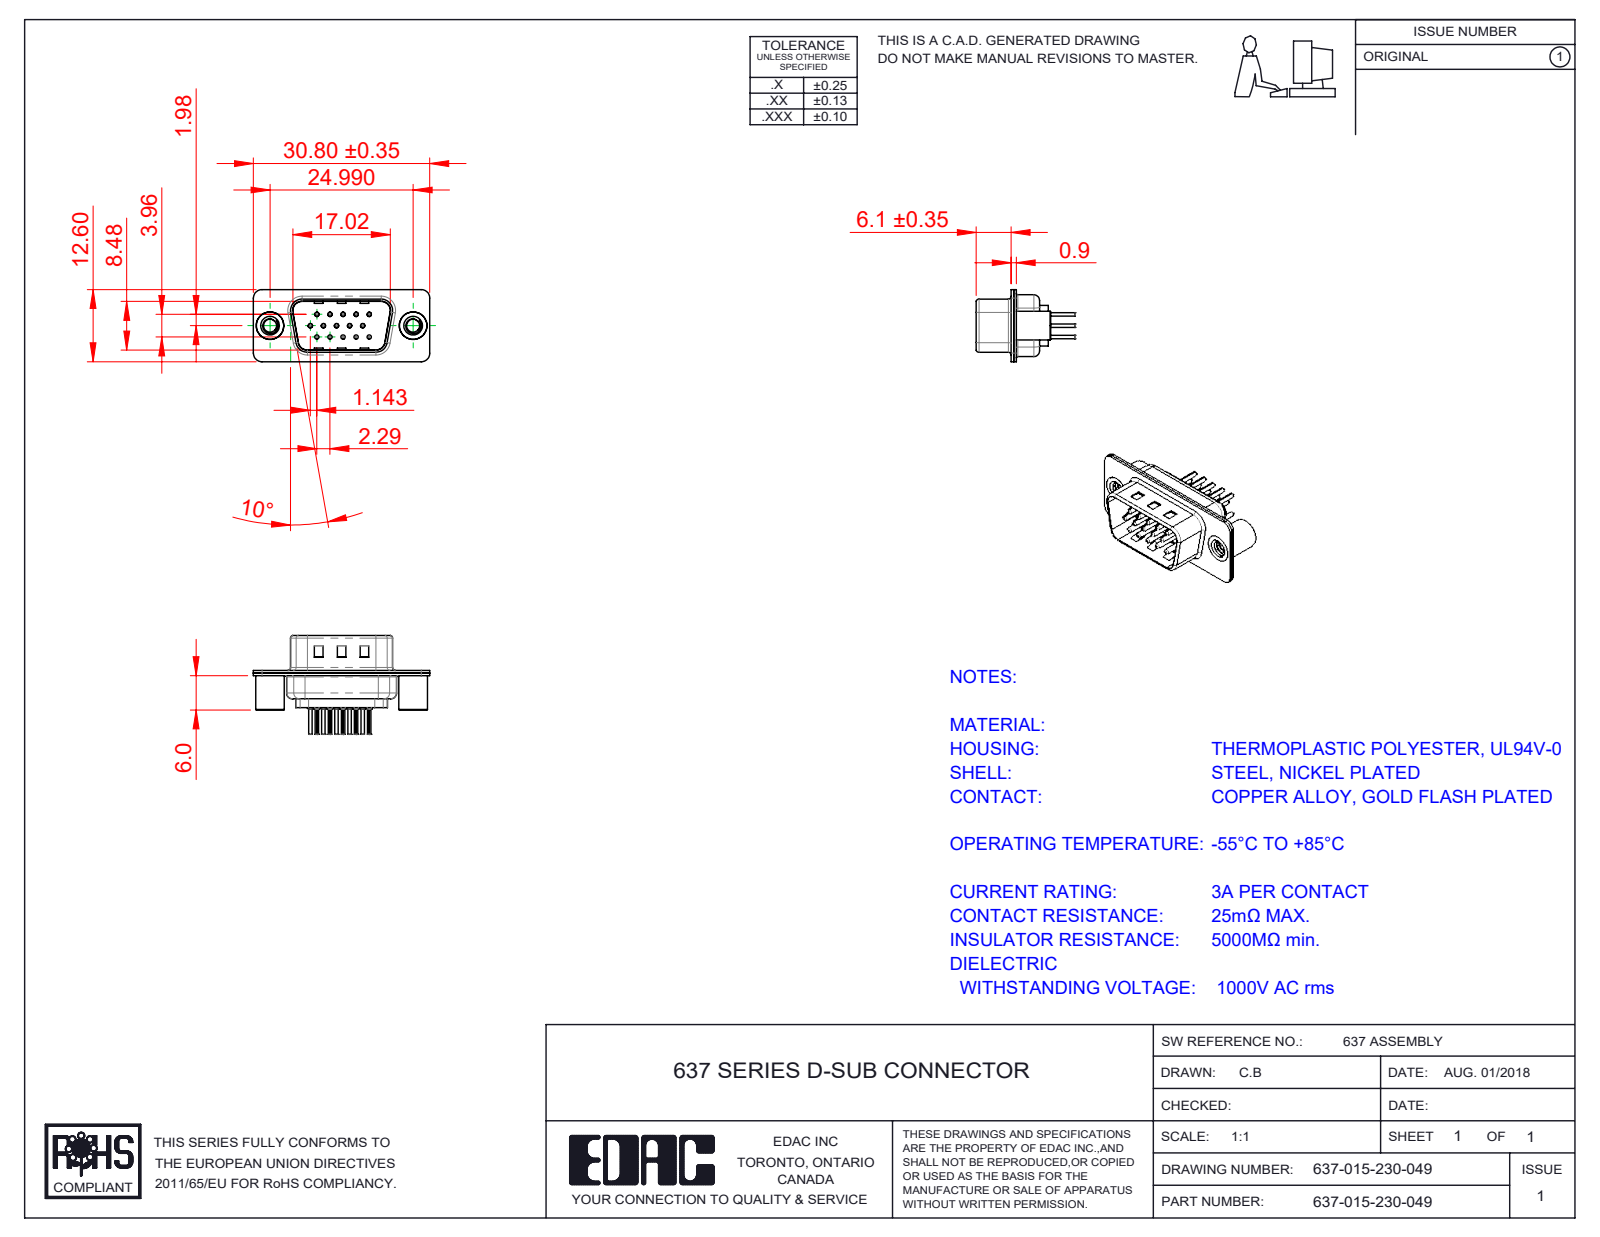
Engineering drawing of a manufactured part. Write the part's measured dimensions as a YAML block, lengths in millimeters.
part_name: "637 Housing_15 Contacts; 637 Contact Row 2_30; 637 Contact Row 3_30; 637 Contact Row 1_30 (+4 more)"
step_written_by: "SolidWorks 2020 (CONFIG_CONTROL_DESIGN)"
units: millimeters
bodies: {solids: 20, faces: 1838, planar: 469, cylindrical: 712, other: 657}
overall_size: [30.8, 17.25, 12.6]
volume: 1379
surface_area: 4840
round_holes:
  - {diameter: 0.2, count: 15}
  - {diameter: 0.35, count: 15}
  - {diameter: 1.1, count: 15}
  - {diameter: 1.6, count: 15}
  - {diameter: 2.26, count: 2}
  - {diameter: 4, count: 2}
  - {diameter: 4.8, count: 2}
round_bosses_or_shafts:
  - {diameter: 2, count: 15}
  - {diameter: 1.5, count: 15}
  - {diameter: 0.75, count: 15}
  - {diameter: 0.6, count: 15}
  - {diameter: 5, count: 2}
  - {diameter: 4.9, count: 2}
  - {diameter: 4.5, count: 2}
partial_cylinders:
  - {radius: 0.1, count: 30}
  - {radius: 1.5, count: 16}
  - {radius: 2, count: 12}
  - {radius: 0.5, count: 8}
  - {radius: 0.25, count: 4}
  - {radius: 0.55, count: 4}
  - {radius: 0.7, count: 4}
  - {radius: 0.95, count: 4}
face_to_face_distances: [0.45, 0.9, 0.4, 0.7, 8.88, 8.48, 1.05, 0.31, 4.55, 1.16]
hole_center_spacings: [3.96, 2.28, 4.57, 2.29, 6.05, 6.86, 7.92, 6.04]
